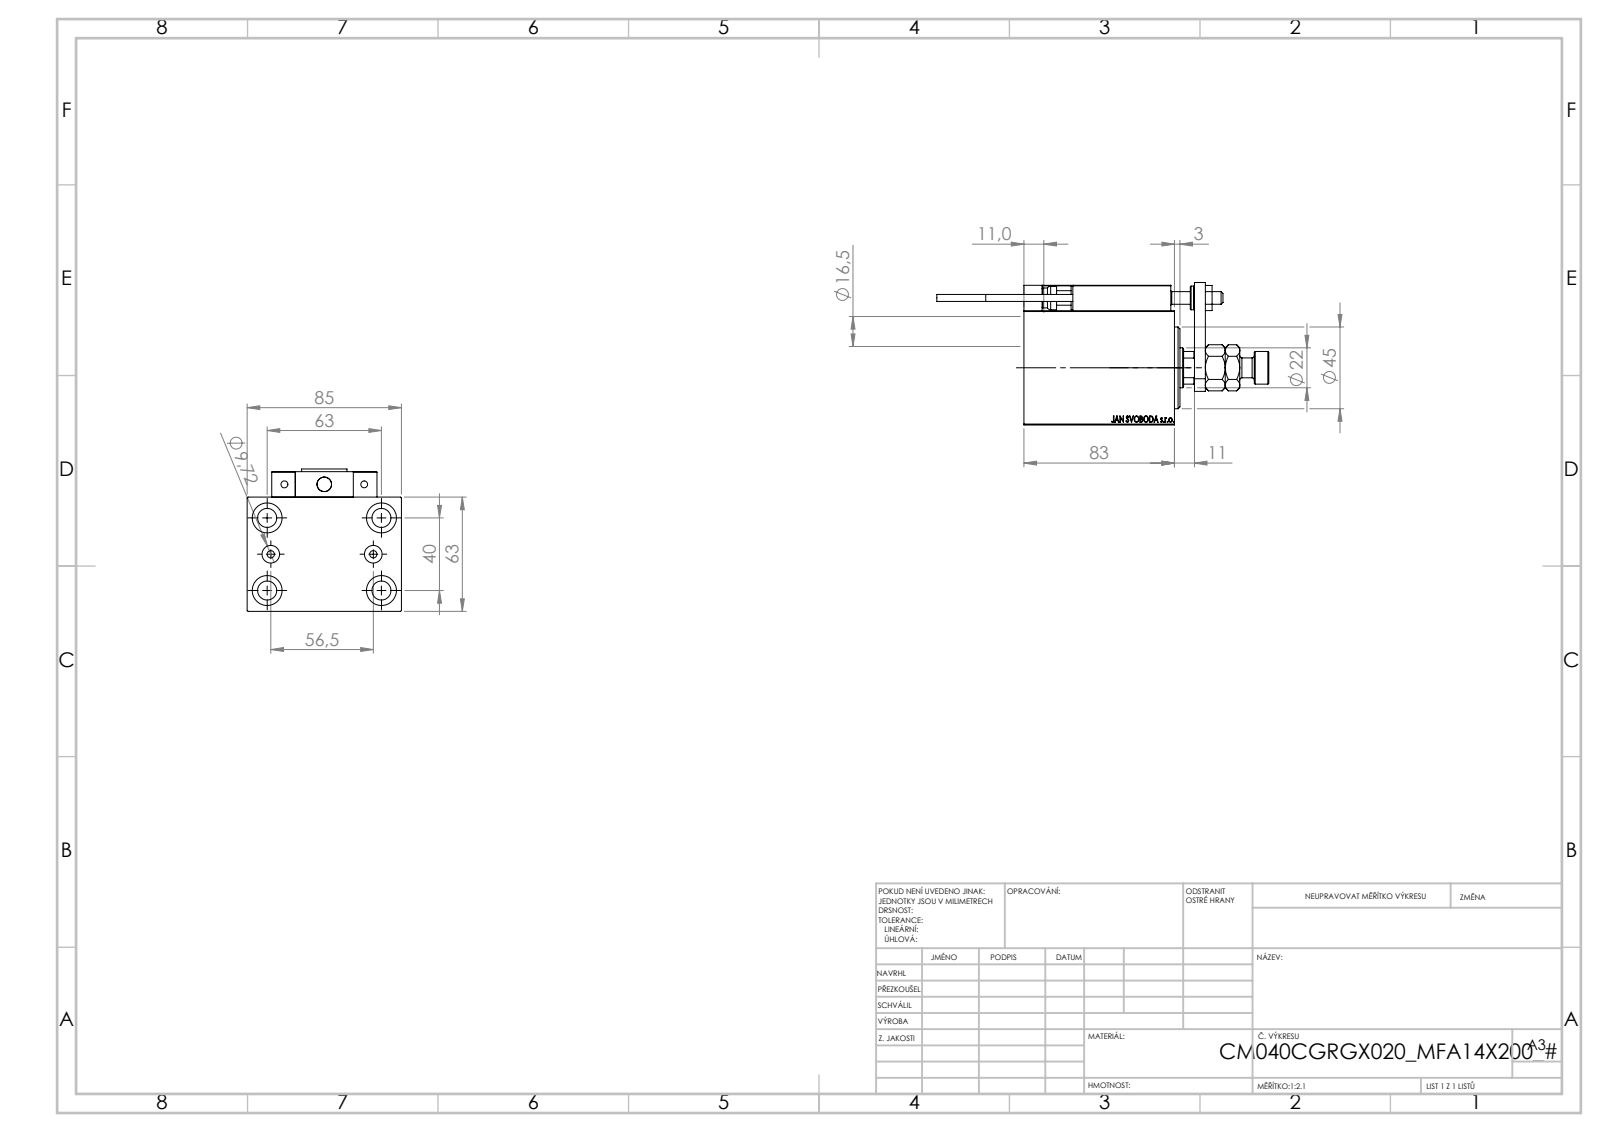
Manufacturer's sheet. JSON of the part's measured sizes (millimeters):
{"part_name": "X_Y_MFA; SWITCH X; KONCOVKA; SWITCH_X_FRONT_BACK (+7 more)", "step_written_by": "SolidWorks 2019 (CONFIG_CONTROL_DESIGN)", "units": "millimeters", "bodies": {"solids": 24, "faces": 1330, "planar": 576, "cylindrical": 188, "other": 566}, "overall_size": [184, 85, 78.5], "volume_mm3": 447770, "surface_area_mm2": 95935, "round_holes": [[4, 6], [8, 5], [16.5, 5], [3.2, 4], [10.5, 4], [5, 2], [9.72, 2], [7, 1], [12.5, 1], [22, 1], [25.5, 1], [40, 1]], "round_bosses_or_shafts": [[11, 2], [5, 2], [3.8, 2], [18, 1], [13, 1]], "partial_cylinders_radius": [[0.3, 30], [3, 2], [10.5, 1]], "face_to_face_distances": [63, 85, 18, 14, 83, 20, 44.5, 10, 38.5, 77], "hole_center_spacings": [20.26, 37.31, 63.01, 11.37, 20, 28.25, 29.59, 29.69]}
